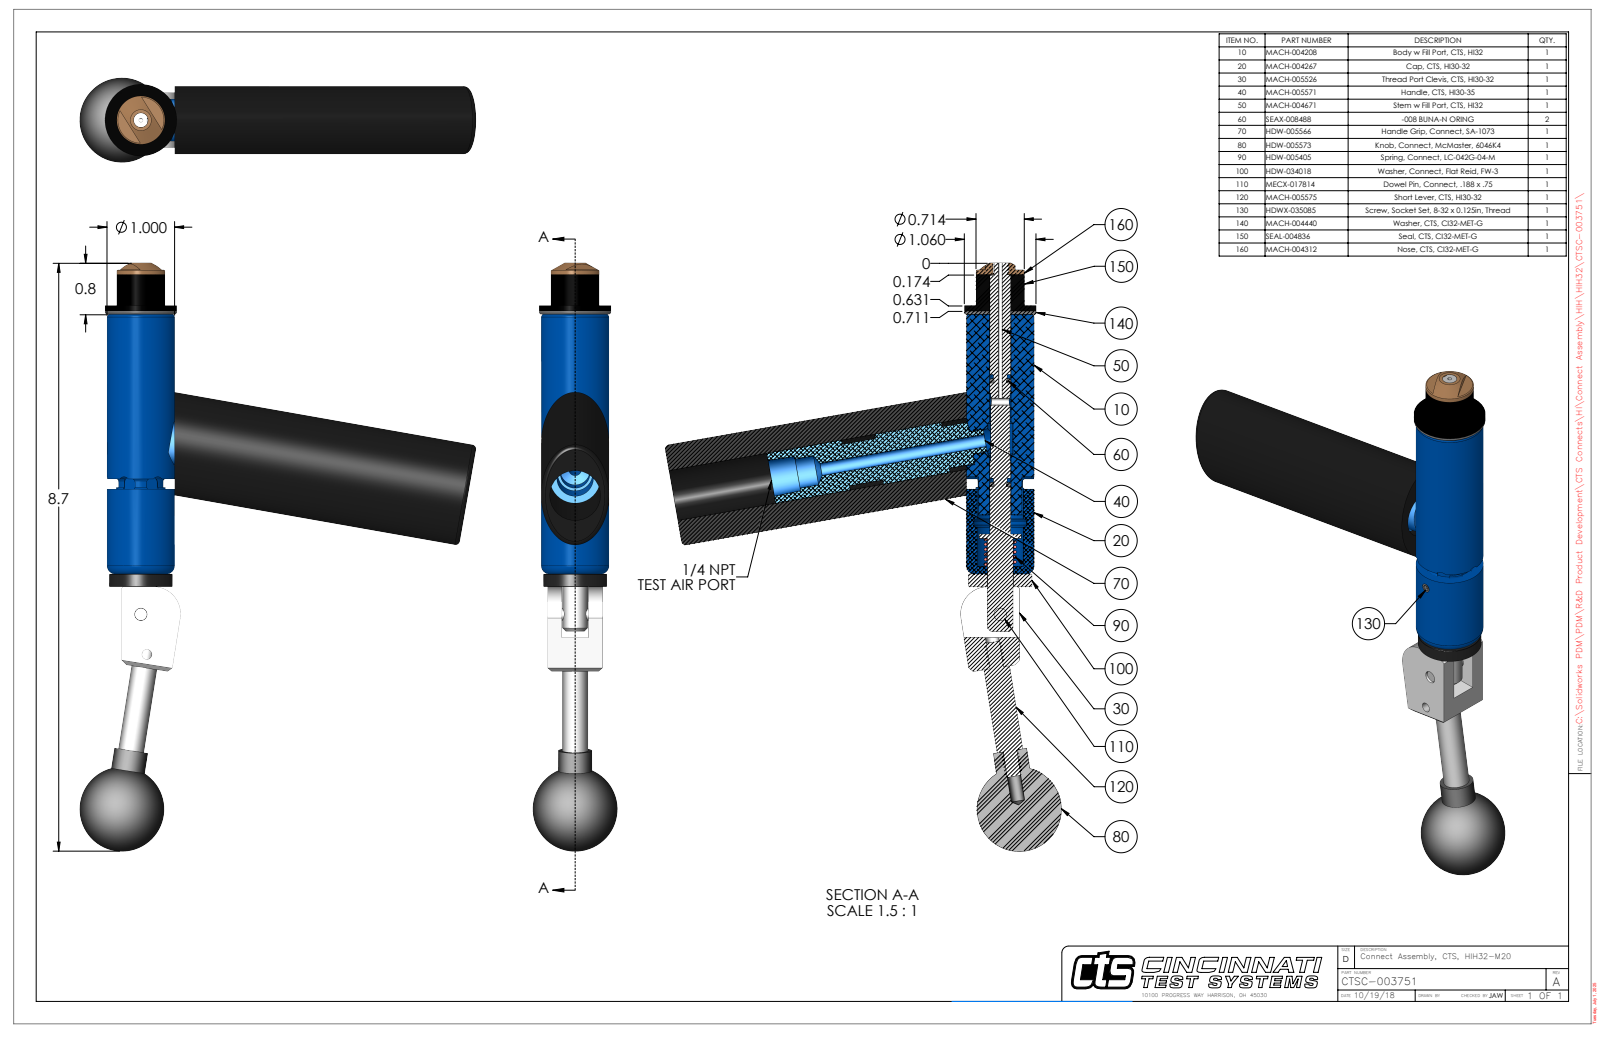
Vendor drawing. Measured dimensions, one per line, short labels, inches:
name: CTSC-003751
written by: SolidWorks 2023 (AUTOMOTIVE_DESIGN)
unit: in
bodies: 10 solids, 309 faces (116 planar, 124 cylindrical, 69 other)
size: 8.704 × 5.856 × 1.25
volume: 9.439 in³; area: 78.39 in²
holes: 2× ⌀0.201, 1× ⌀0.063, 1× ⌀0.109, 1× ⌀0.136, 1× ⌀0.15, 1× ⌀0.187, 1× ⌀0.189, 1× ⌀0.213, 1× ⌀0.31, 1× ⌀0.314, 1× ⌀0.316, 1× ⌀0.385
bosses: 2× ⌀0.25, 2× ⌀0.201, 1× ⌀1.06, 1× ⌀1, 1× ⌀0.936, 1× ⌀0.75, 1× ⌀0.714, 1× ⌀0.62
rounds: 6× R0.093, 2× R0.029, 1× R0.07, 1× R0.325, 1× R0.375, 1× R0.4, 1× R0.463
face distances: 0.05, 0.21, 0.602, 3.883, 3.833, 0.812, 0.537, 0.587, 4.42, 4.608
hole spacings: 0.599, 1.658, 2.252
